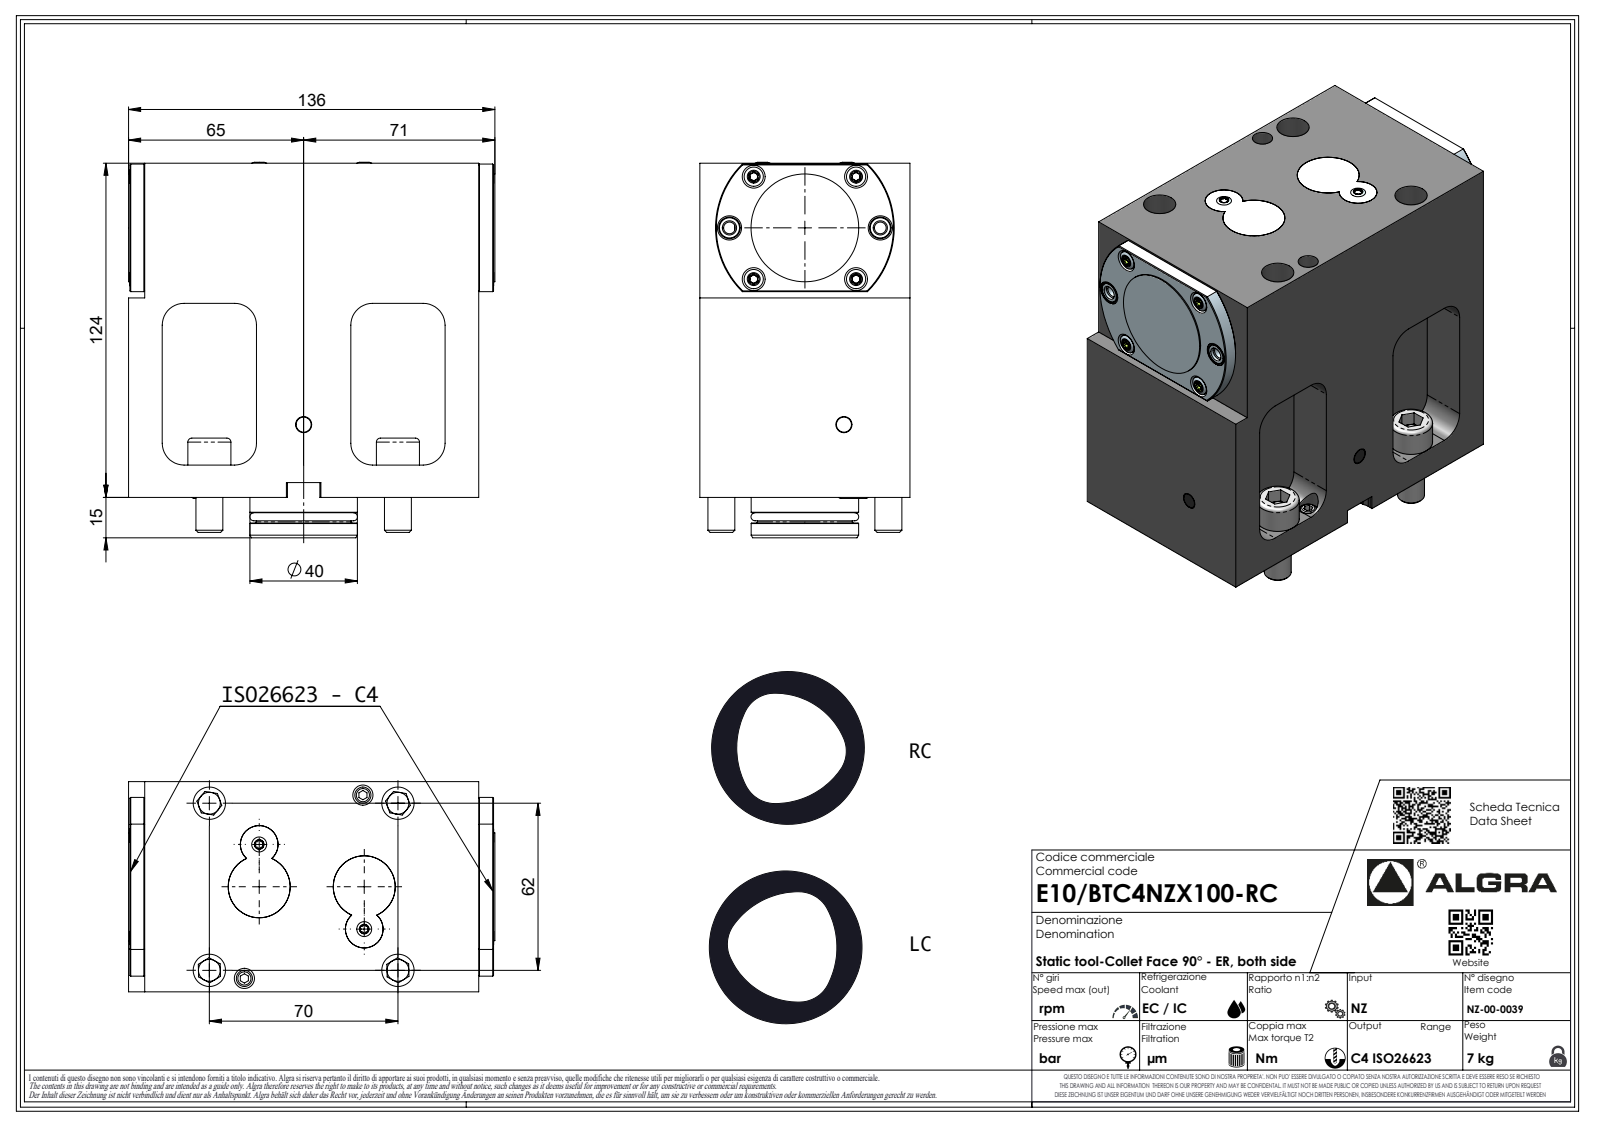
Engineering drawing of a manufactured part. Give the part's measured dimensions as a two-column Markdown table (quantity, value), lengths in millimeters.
| quantity | value |
| --- | --- |
| part name | E10BTC4NZX100-RC |
| STEP written by | SolidWorks 2023 (AUTOMOTIVE_DESIGN) |
| units | millimeters |
| bodies | 1 solid, 694 faces (334 planar, 199 cylindrical, 161 other) |
| overall size | 139 × 136 × 78 |
| volume | 1 285 000 mm³ |
| surface area | 78 973 mm² |
| round holes (diameter × count) | 4.35 × 2, 5.3 × 2, 8.01 × 2, 9 × 2, 2.1 × 1 |
| round bosses / shafts (diameter × count) | 10 × 4, 7.15 × 4, 40 × 1, 39.9 × 1, 35.2 × 1, 6.37 × 1, 1.7 × 1 |
| partial cylindrical surfaces (radius × count) | 0.33 × 24, 0.83 × 24, 5 × 8, 0.33 × 7, 0.52 × 7, 3.7 × 7, 1.42 × 4, 0.21 × 1 |
| main face-to-face distances | 78, 124, 130, 5.5, 0.5, 135.5, 6, 129.5, 15, 136 |
| hole center spacings | 56 |
